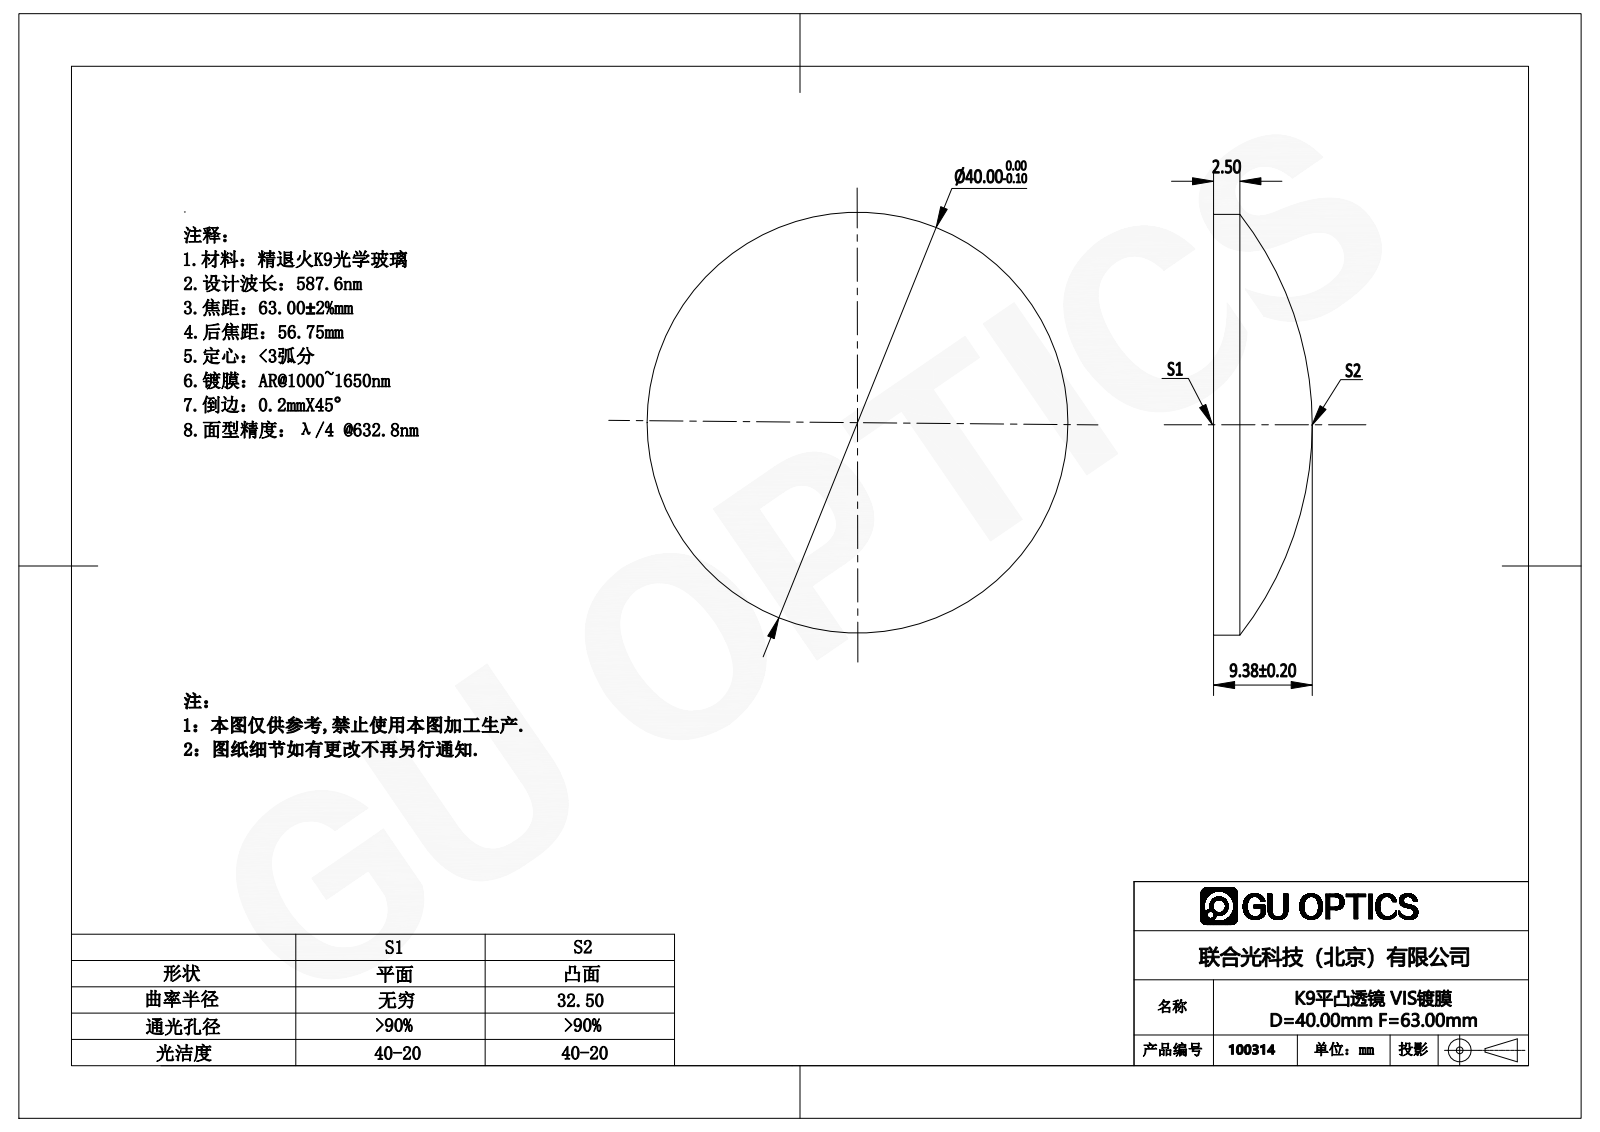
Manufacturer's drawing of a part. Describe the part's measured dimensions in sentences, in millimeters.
The part is named "100142". Its 3-D file was written by "SolidWorks 2016 (AUTOMOTIVE_DESIGN)". It is 1 solid with 5 faces: 1 planar, 2 cylindrical and 2 other. Overall it measures 40 by 40 by 9.38 millimeters. Its volume is 7 635 cubic millimeters and its surface area 2 976 square millimeters. Round bosses or shafts: 1 of diameter 40.
